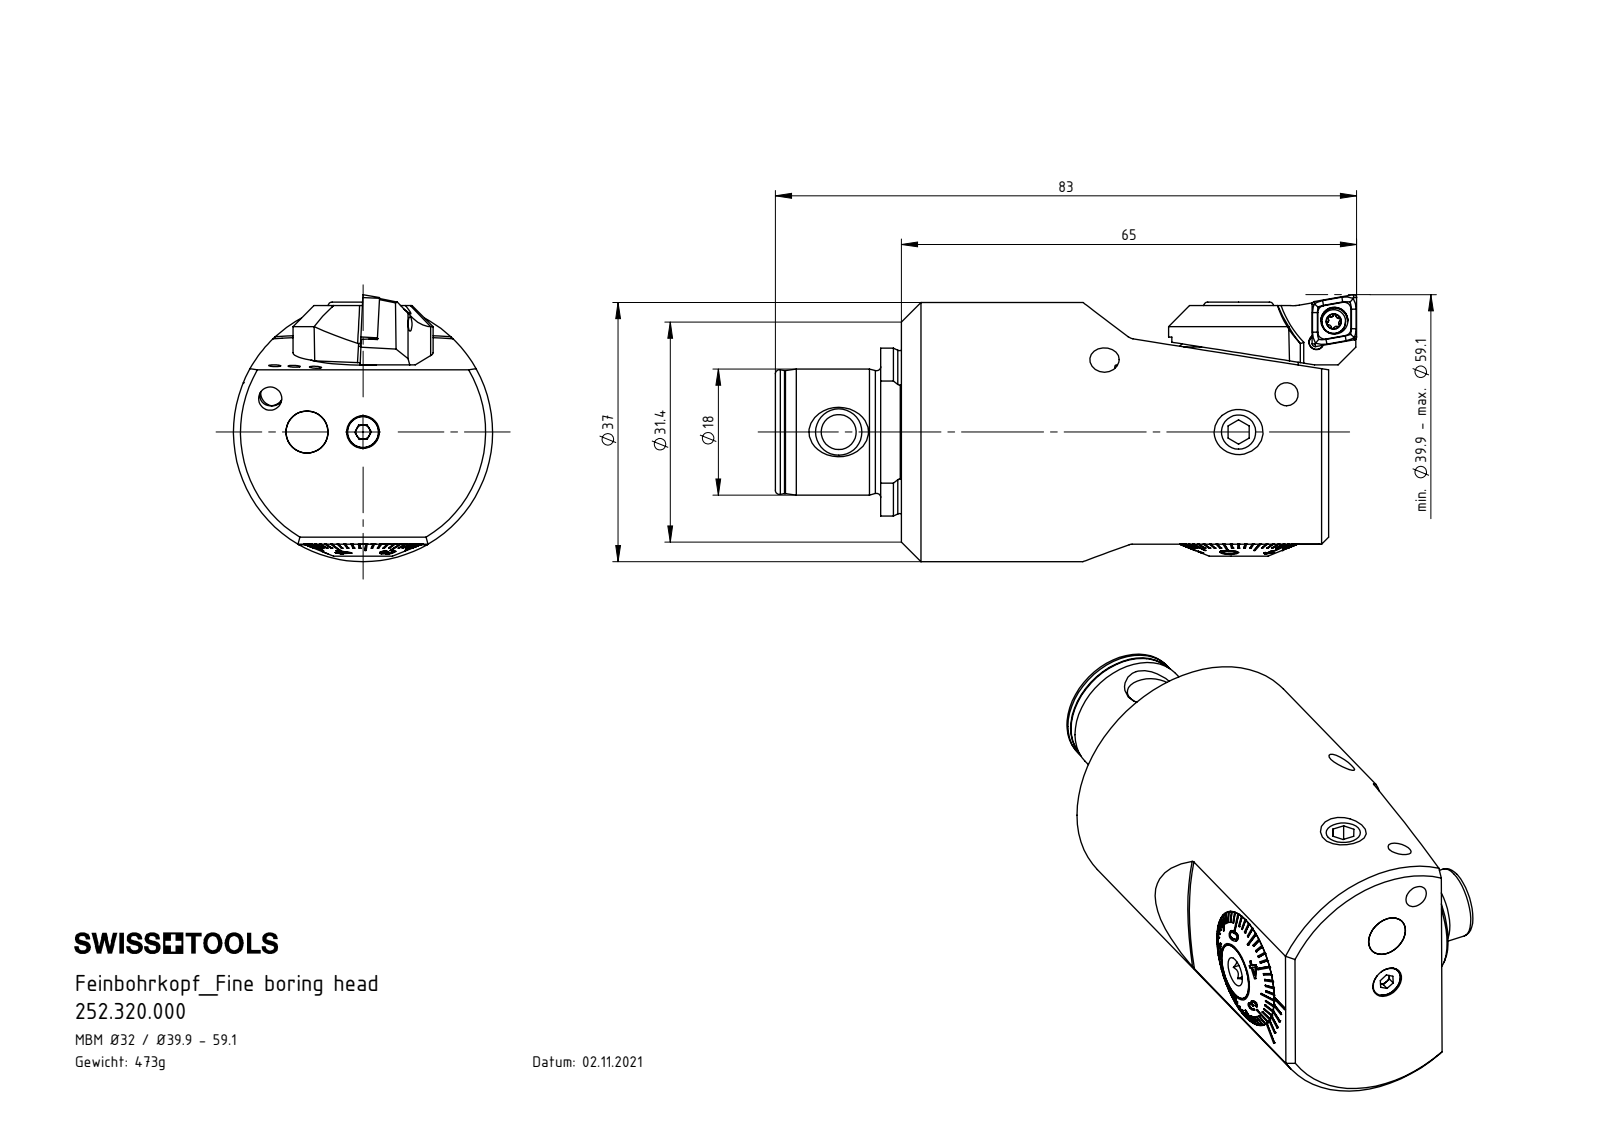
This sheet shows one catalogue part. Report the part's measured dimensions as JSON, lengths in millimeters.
{"part_name": "MB3.F32.K21.065; F32-BG3.006.026_A; F32-BG1.012.017; F32-BG1.010.006_A (+7 more)", "step_written_by": "SolidWorks 2012 (CONFIG_CONTROL_DESIGN)", "units": "millimeters", "bodies": {"solids": 9, "faces": 598, "planar": 258, "cylindrical": 96, "other": 244}, "overall_size": [79, 32, 32], "volume_mm3": 46941, "surface_area_mm2": 16813, "round_holes": [[2.5, 5], [5, 3], [8.5, 2], [2.05, 1], [2.7, 1], [2.9, 1], [3, 1], [6, 1], [7, 1], [7.4, 1], [10.3, 1], [14, 1]], "round_bosses_or_shafts": [[32, 1], [18, 1], [17, 1], [16.98, 1], [16.85, 1], [14.65, 1], [10, 1], [8, 1]], "partial_cylinders_radius": [[0.5, 2], [1.75, 2], [1, 1], [1.9, 1], [3.2, 1], [11.97, 1]], "face_to_face_distances": [61, 0.8, 3.7, 4.5, 2.2, 1.5, 2.3, 25.35, 18, 79], "hole_center_spacings": [5.7, 8, 11.68, 25.15, 57.1]}
